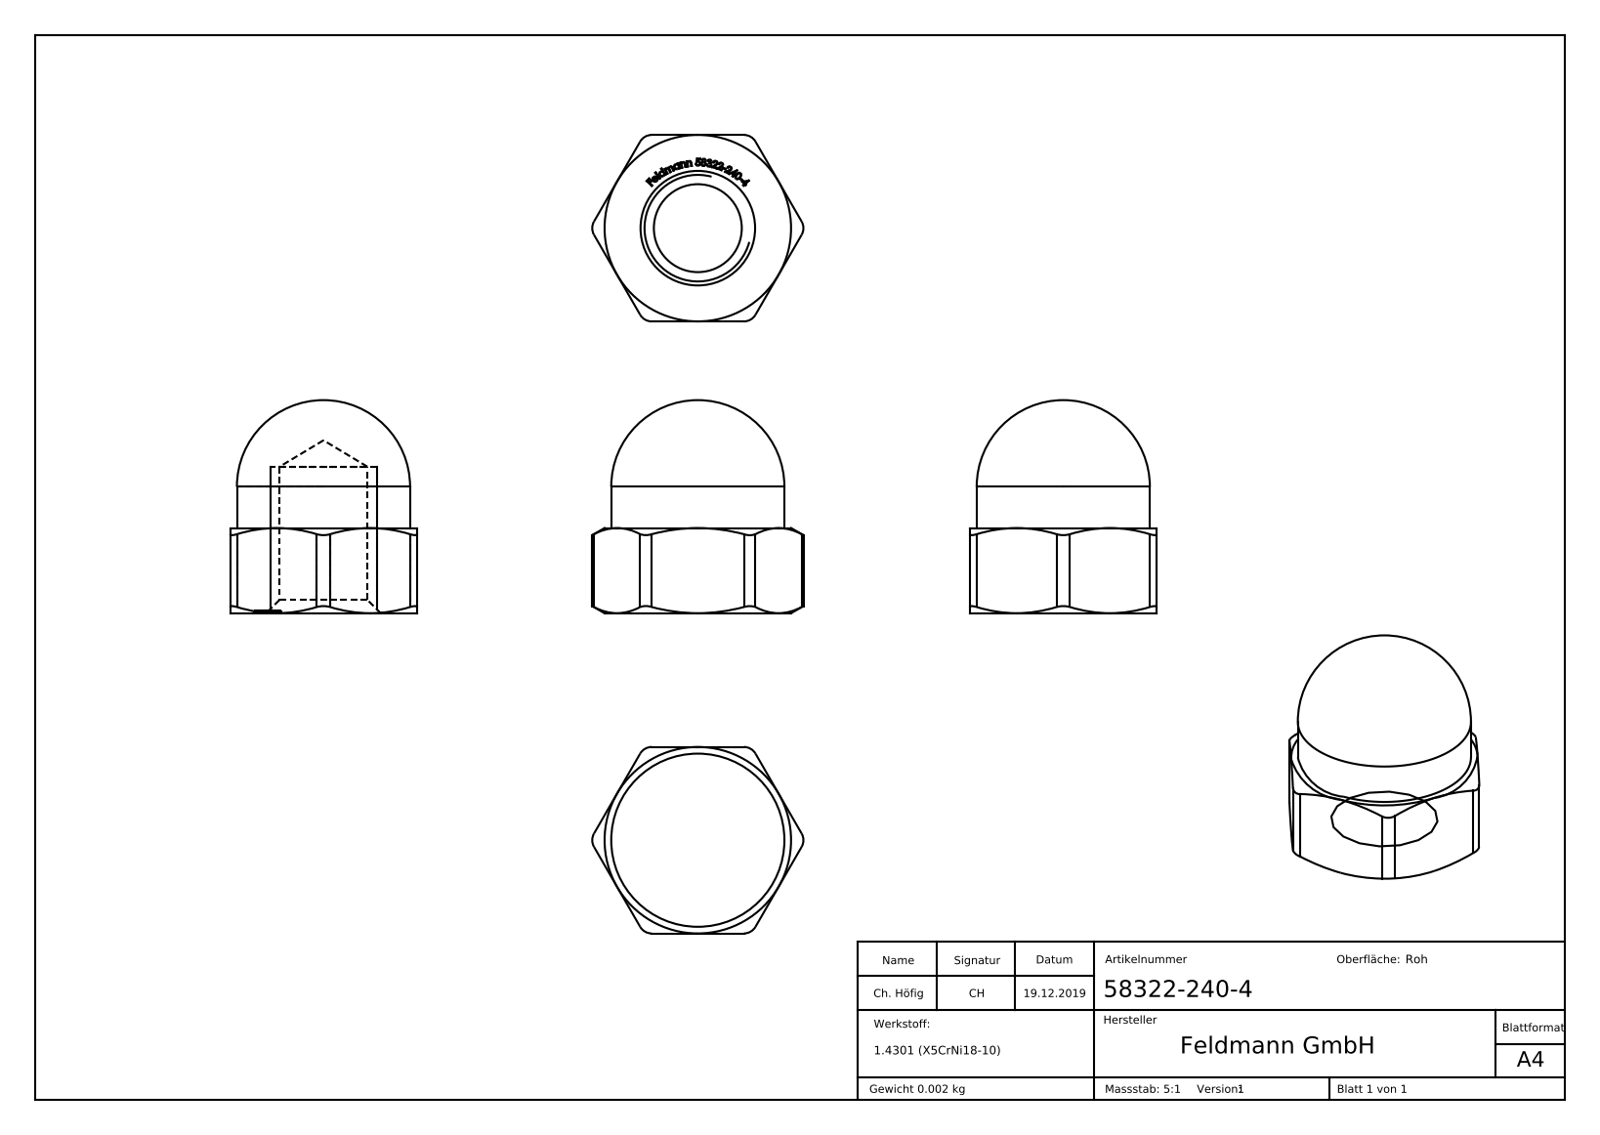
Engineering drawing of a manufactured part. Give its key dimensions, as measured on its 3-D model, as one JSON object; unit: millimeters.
{"part_name": "58322-240-4", "step_written_by": "SolidWorks 2015 (CONFIG_CONTROL_DESIGN)", "units": "millimeters", "bodies": {"solids": 1, "faces": 287, "planar": 142, "cylindrical": 8, "other": 137}, "overall_size": [13, 7.93, 7], "volume_mm3": 207, "surface_area_mm2": 280, "round_holes": [[3.3, 1]], "round_bosses_or_shafts": [[6.5, 1]], "partial_cylinders_radius": [[0.5, 6]], "face_to_face_distances": [7, 3.2, 3.1]}
